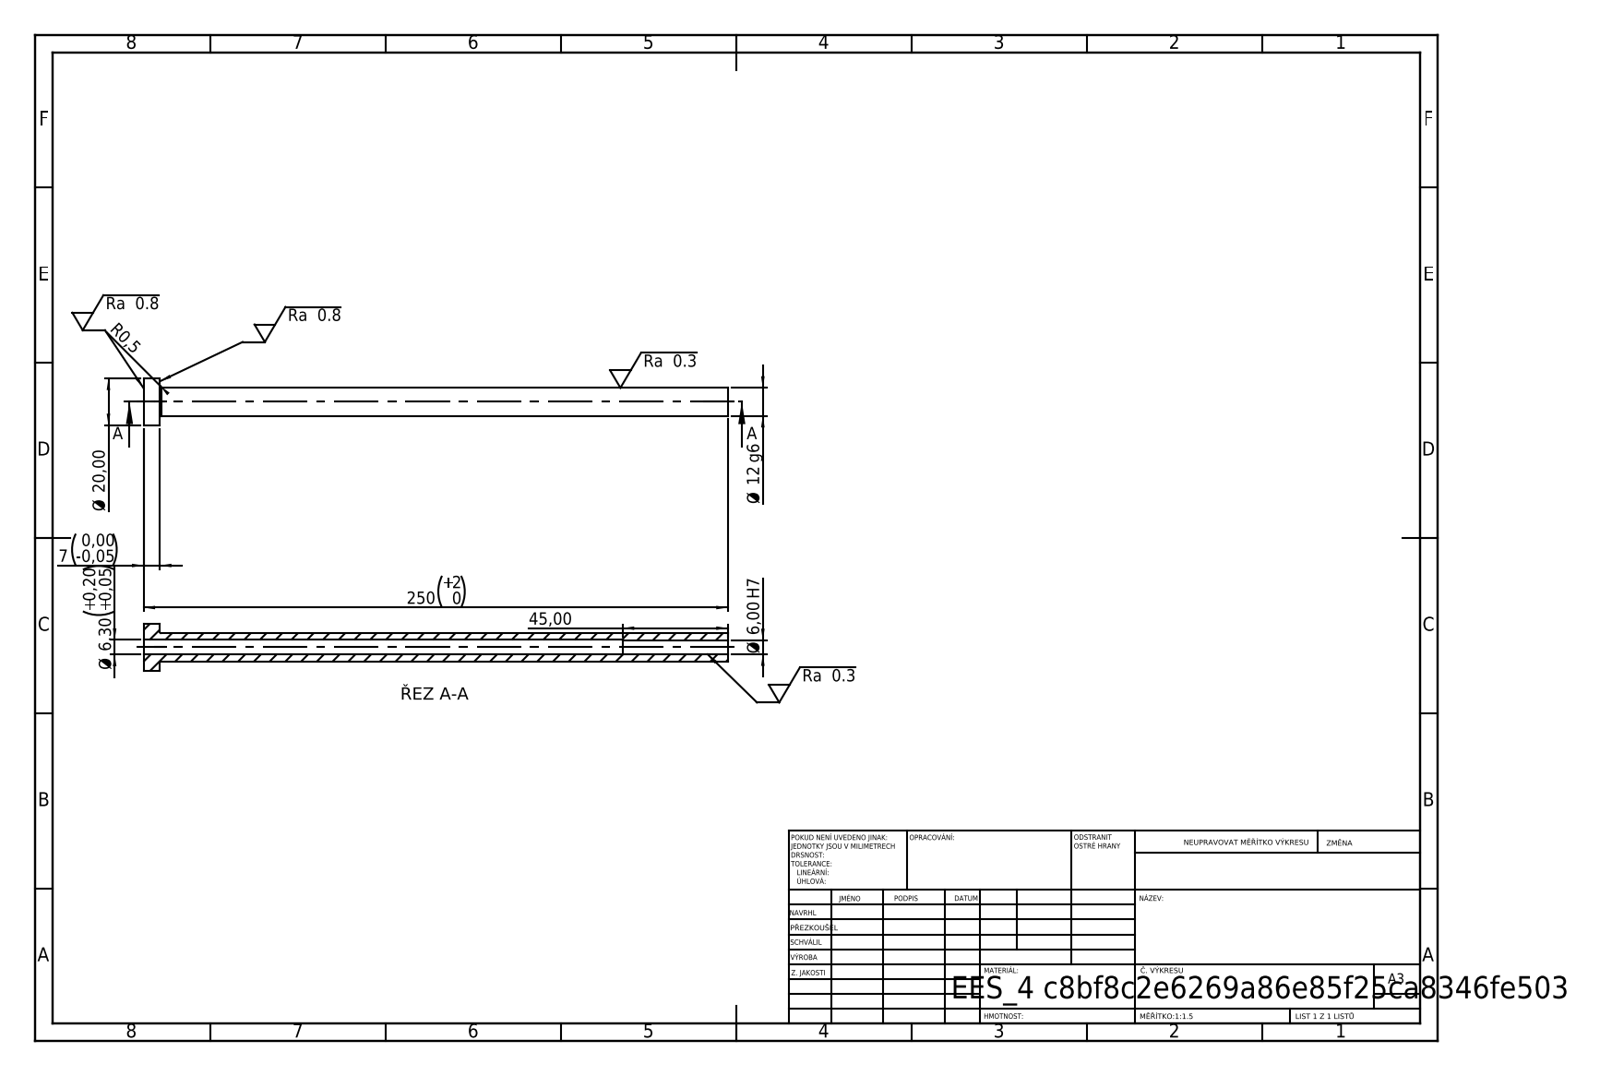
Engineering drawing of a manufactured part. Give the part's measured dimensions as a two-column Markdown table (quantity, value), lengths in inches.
| quantity | value |
| --- | --- |
| STEP written by | SolidWorks 2019 (CONFIG_CONTROL_DESIGN) |
| units | inches |
| bodies | 1 solid, 14 faces (4 planar, 8 cylindrical, 2 other) |
| overall size | 9.843 × 0.787 × 0.787 |
| volume | 1.344 in³ |
| surface area | 23.36 in² |
| round holes (diameter × count) | 0.236 × 1, 0.248 × 1 |
| round bosses / shafts (diameter × count) | 0.787 × 1, 0.472 × 1 |
| main face-to-face distances | 0.276, 9.843, 9.567, 8.071, 7.795, 1.772 |
